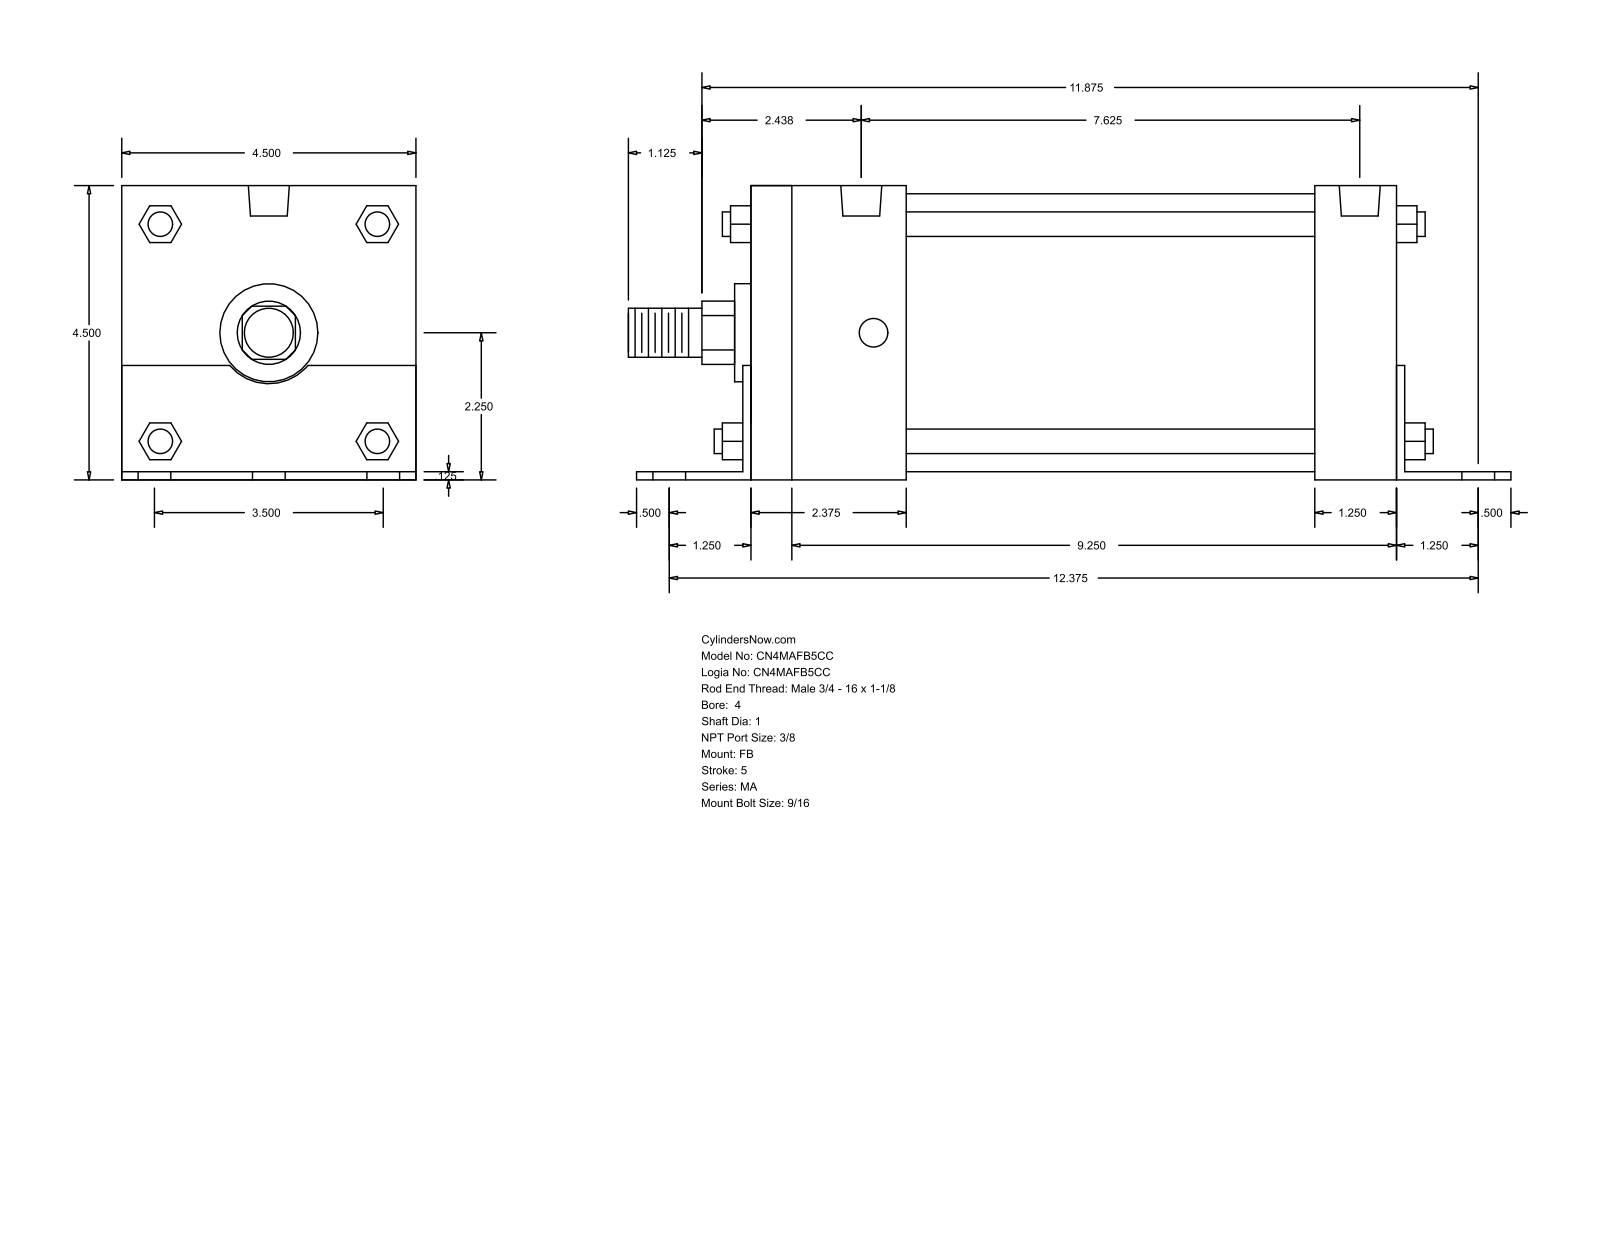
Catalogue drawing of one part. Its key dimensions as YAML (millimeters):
part_name: "MA_FB__0400_1"
step_written_by: "GSSL Pune (CONFIG_CONTROL_DESIGN)"
units: millimeters
bodies: {solids: 0, faces: 140, planar: 105, cylindrical: 35, other: 0}
overall_size: [342.9, 114.35, 114.3]
round_holes:
  - {diameter: 14.29, count: 6}
  - {diameter: 11.11, count: 4}
  - {diameter: 15.93, count: 2}
round_bosses_or_shafts:
  - {diameter: 9.53, count: 4}
  - {diameter: 107.95, count: 1}
  - {diameter: 38.1, count: 1}
  - {diameter: 25.4, count: 1}
  - {diameter: 19.05, count: 1}
partial_cylinders:
  - {radius: 12.29, count: 1}
  - {radius: 19.81, count: 1}
face_to_face_distances: [114.3, 3.17, 114.35, 254, 3.12, 111.18, 250.83, 257.17, 34.93, 222.24]
hole_center_spacings: [44.45, 317.45, 314.32, 63.99, 67.5, 86.85, 88.9, 90.97]
